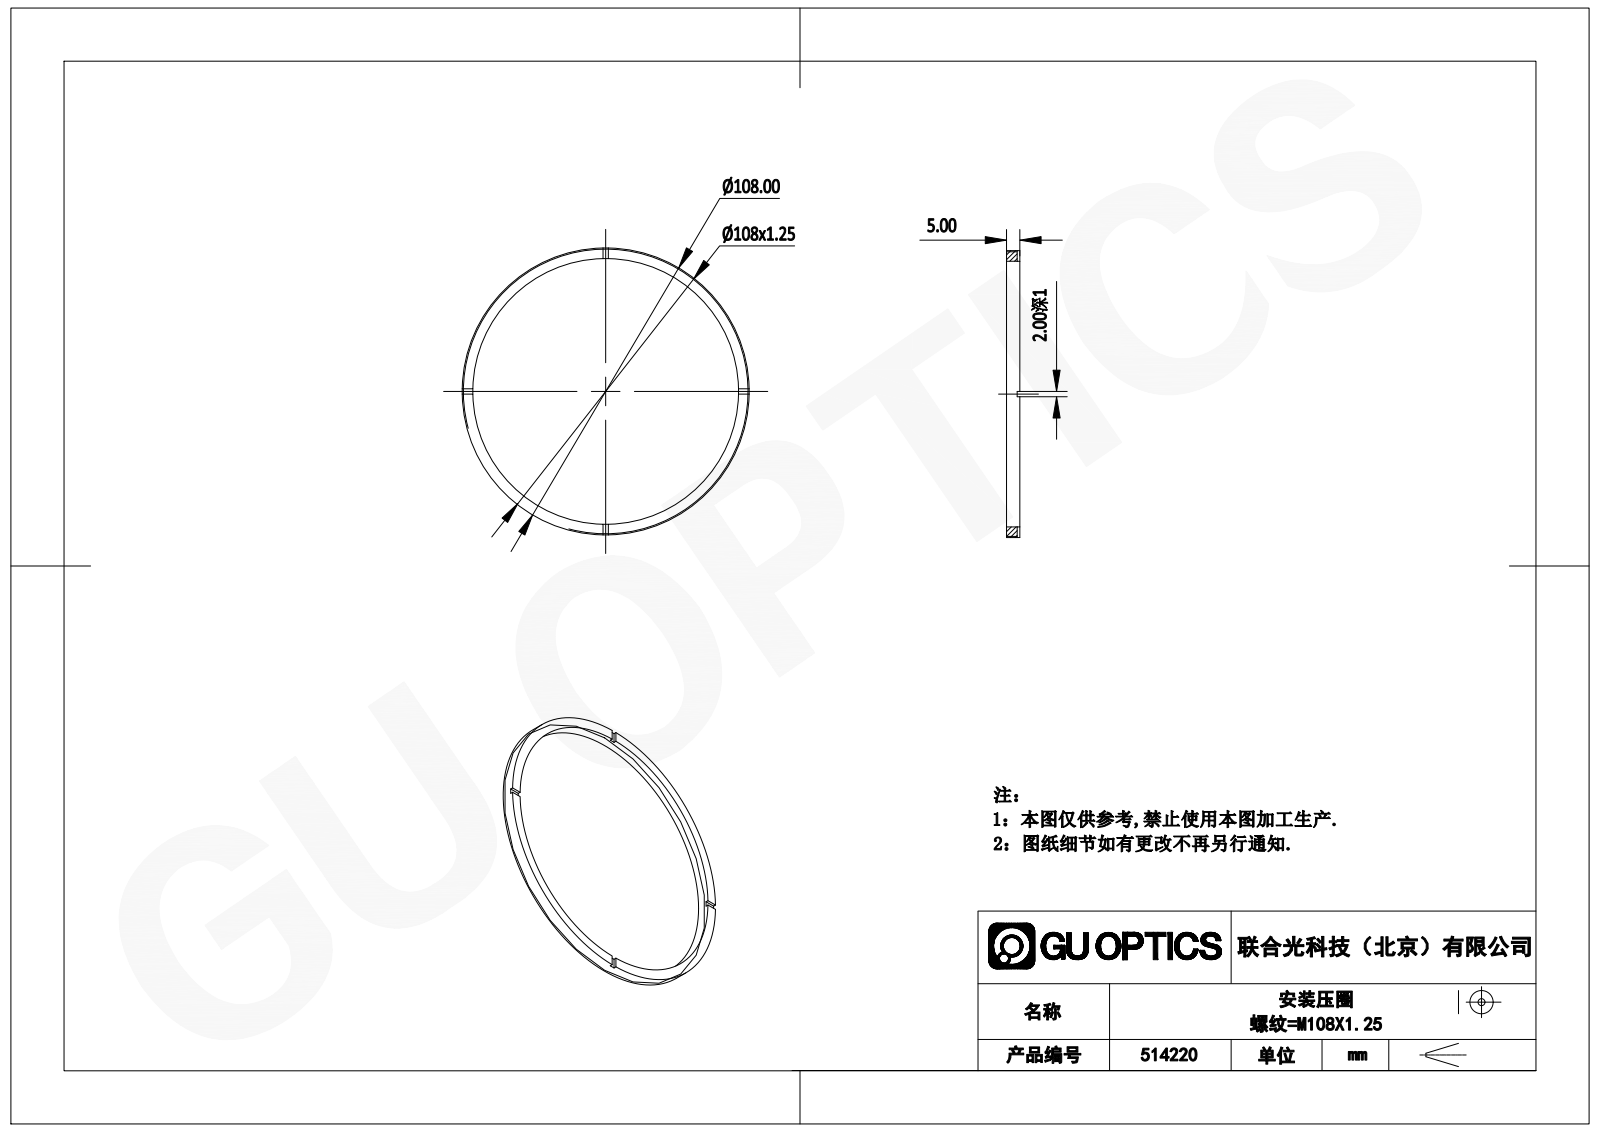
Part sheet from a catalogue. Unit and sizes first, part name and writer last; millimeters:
Units: millimetres
Overall size (bounding box): 108 × 108 × 5
Round holes (diameter × count): ⌀100 ×1
Round bosses / shafts (diameter × count): ⌀108 ×1
Main face-to-face distances: 5, 4, 1, 2
Volume: 6 503 mm³ · Surface area: 5 897 mm²
Bodies: 1 solid, 21 faces (17 planar, 4 cylindrical, 0 other)
Part name (STEP PRODUCT): 514220
STEP written by: SolidWorks 2020 (CONFIG_CONTROL_DESIGN)
